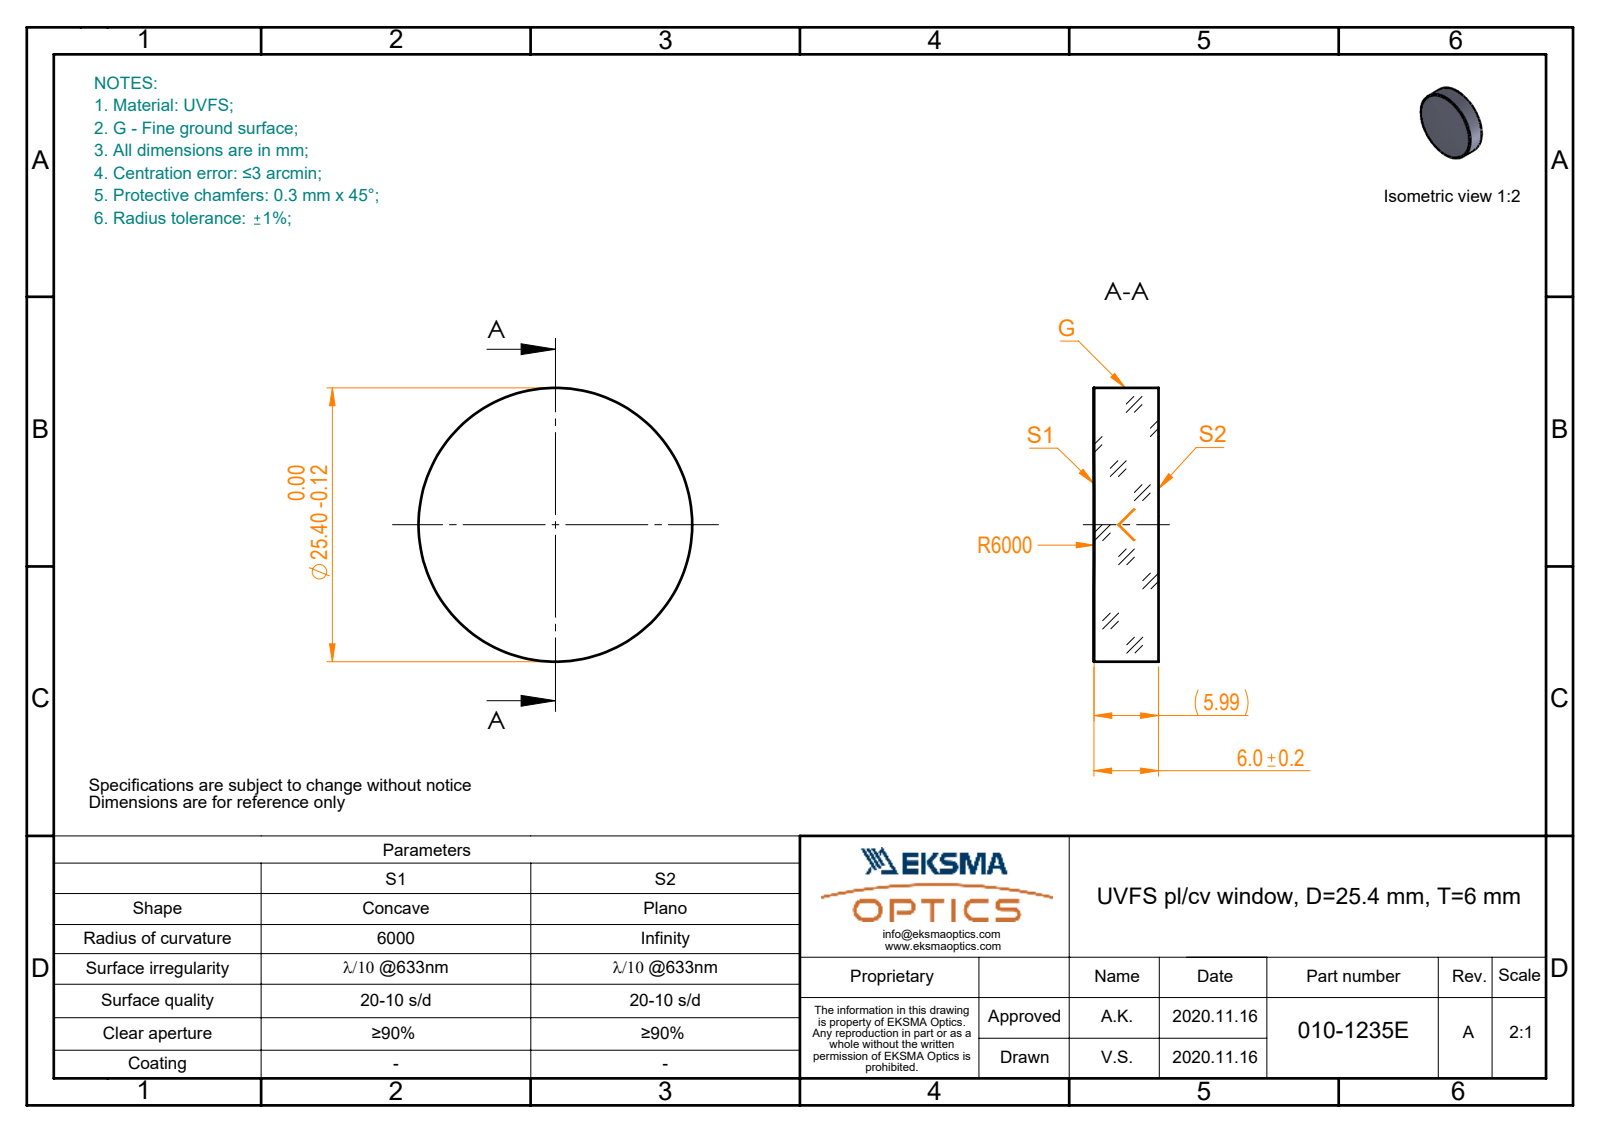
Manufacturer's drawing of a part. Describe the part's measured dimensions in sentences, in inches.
The part is named "010-1235E_UVFS_PCV_window". Its 3-D file was written by "SolidWorks 2019 (CONFIG_CONTROL_DESIGN)". It is 1 solid with 5 faces: 1 planar, 2 cylindrical and 2 other. Overall it measures 1 by 1 by 0.236 inches. Its volume is 0.185 cubic inches and its surface area 2.313 square inches. Round bosses or shafts: 1 of diameter 1.
